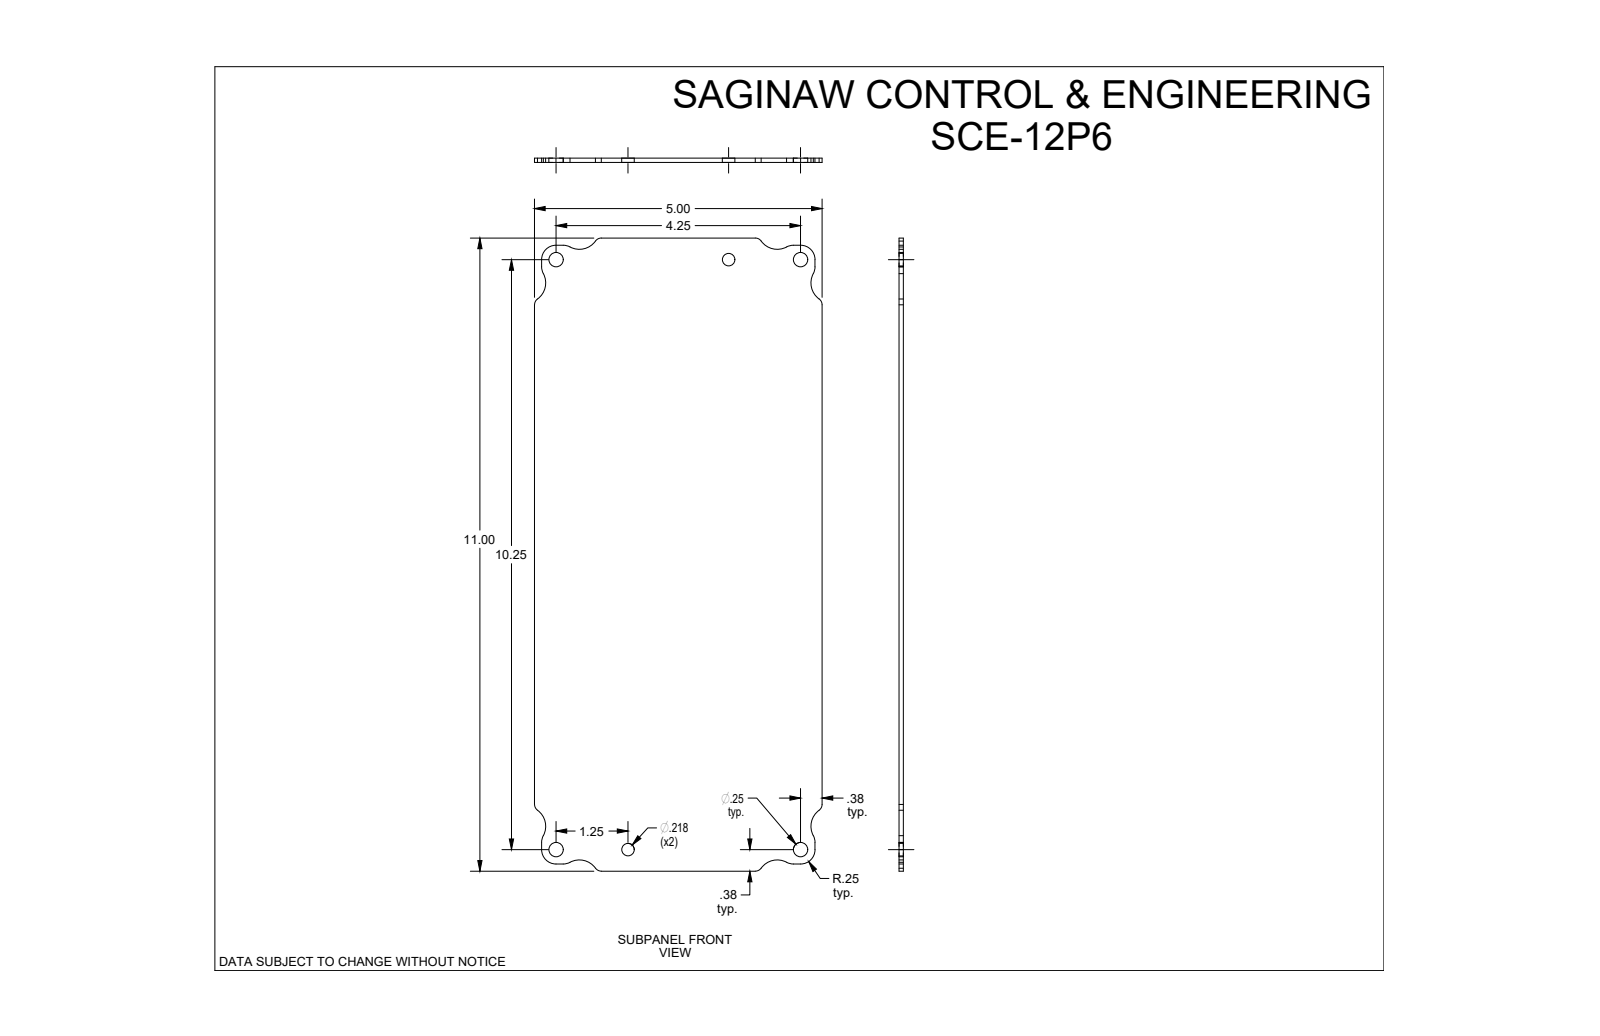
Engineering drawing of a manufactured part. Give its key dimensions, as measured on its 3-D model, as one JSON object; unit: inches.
{"part_name": "SCE-12P6", "step_written_by": "SolidWorks 2019 (CONFIG_CONTROL_DESIGN)", "units": "inches", "bodies": {"solids": 1, "faces": 48, "planar": 14, "cylindrical": 34, "other": 0}, "overall_size": [11, 5, 0.075], "volume_in3": 4.014, "surface_area_in2": 109.7, "round_holes": [[0.25, 4], [0.218, 2]], "partial_cylinders_radius": [[0.25, 12], [0.125, 8], [0.344, 8]], "face_to_face_distances": [0.075, 5, 11, 0.125, 10.875, 0.124, 4.876, 10.75, 4.752], "hole_center_spacings": [1.25, 3, 4.25, 10.25, 10.326, 10.68, 11.096, 10.398]}
